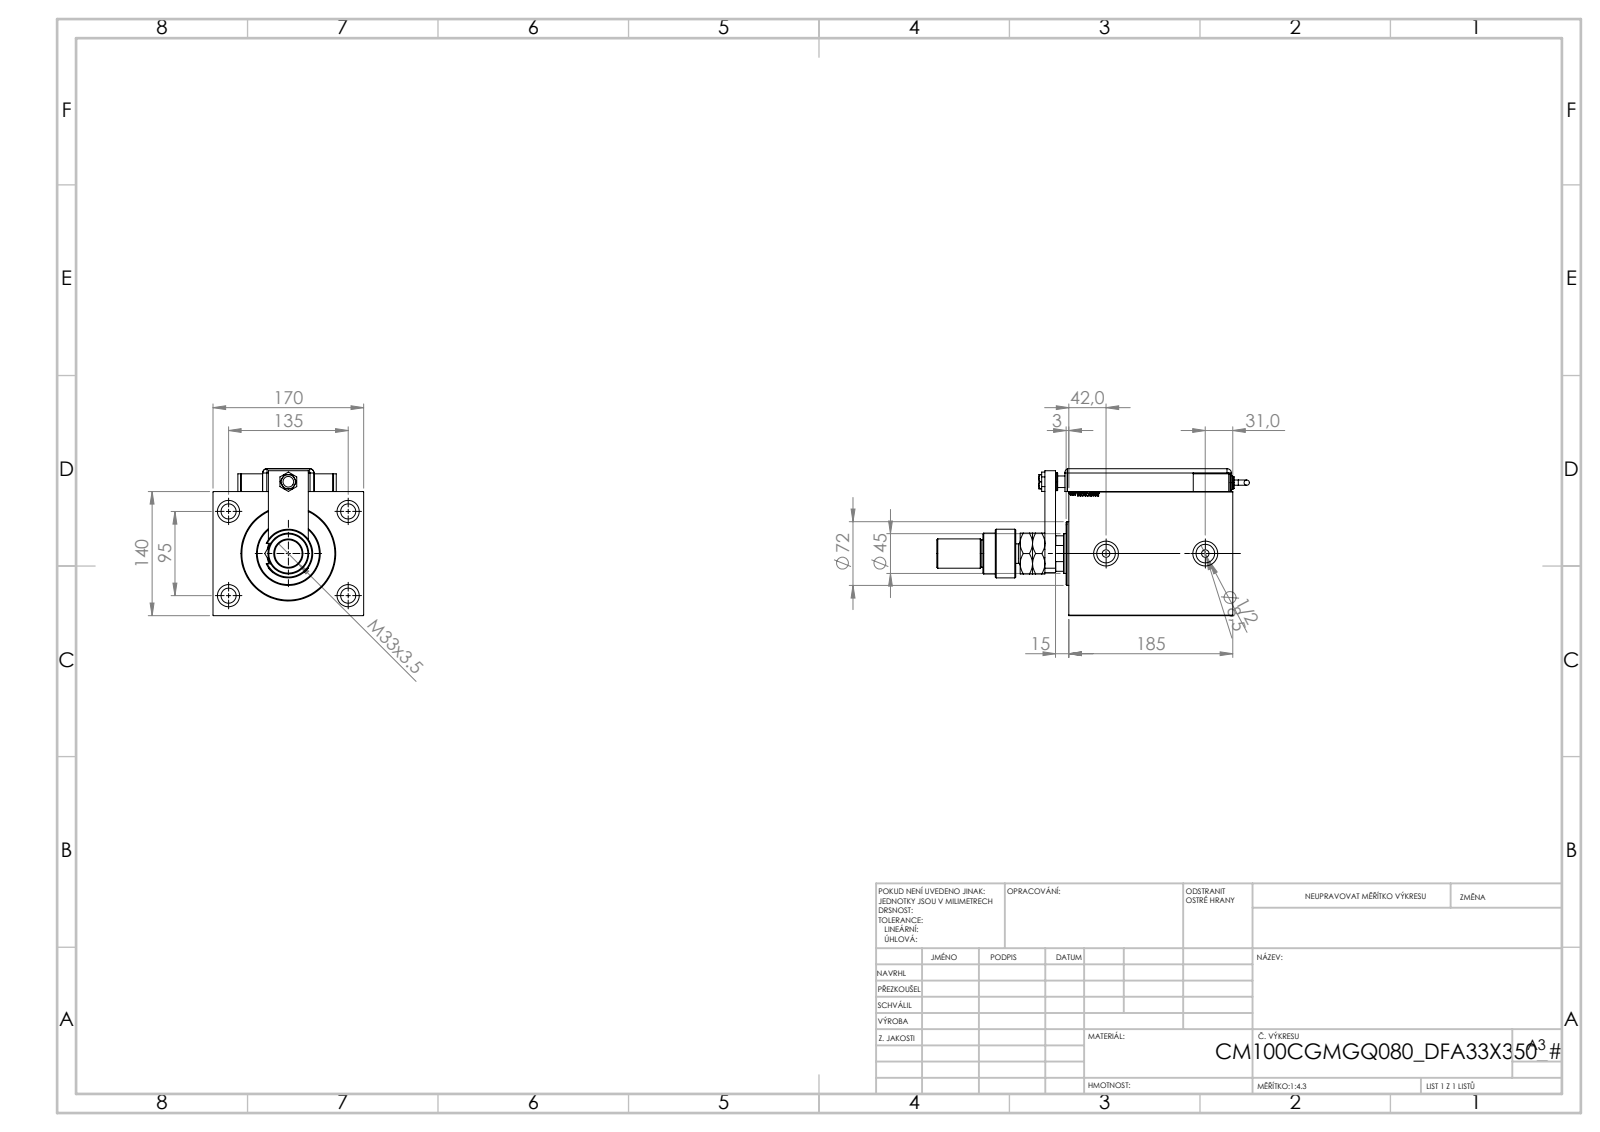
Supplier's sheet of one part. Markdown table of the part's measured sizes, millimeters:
| quantity | value |
| --- | --- |
| part name | V450CM_C_VCP; V450CM_C_Body; SWITCH_Q_FRONT_BACK; MAGNETIC SWITCH Q (+8 more) |
| STEP written by | SolidWorks 2019 (CONFIG_CONTROL_DESIGN) |
| units | millimeters |
| bodies | 15 solids, 1335 faces (644 planar, 130 cylindrical, 561 other) |
| overall size | 352.76 × 170 × 165.8 |
| volume | 4 060 000 mm³ |
| surface area | 421 950 mm² |
| round holes (diameter × count) | 17 × 4, 25 × 4, 4 × 2, 8 × 2, 8.5 × 2, 20.96 × 2, 28 × 2, 12 × 1, 13 × 1, 14 × 1, 31.5 × 1, 33 × 1 |
| round bosses / shafts (diameter × count) | 20 × 3, 16 × 2, 14 × 2, 6 × 2, 72 × 1, 55 × 1, 46 × 1, 35 × 1 |
| partial cylindrical surfaces (radius × count) | 5 × 9, 10 × 1, 11.5 × 1, 22 × 1 |
| main face-to-face distances | 140, 170, 185, 3, 118.75, 66.25, 165.8, 25.8, 12, 10 |
| hole center spacings | 82.54, 75.36, 95, 135, 145.15, 165.08, 20, 81 |
